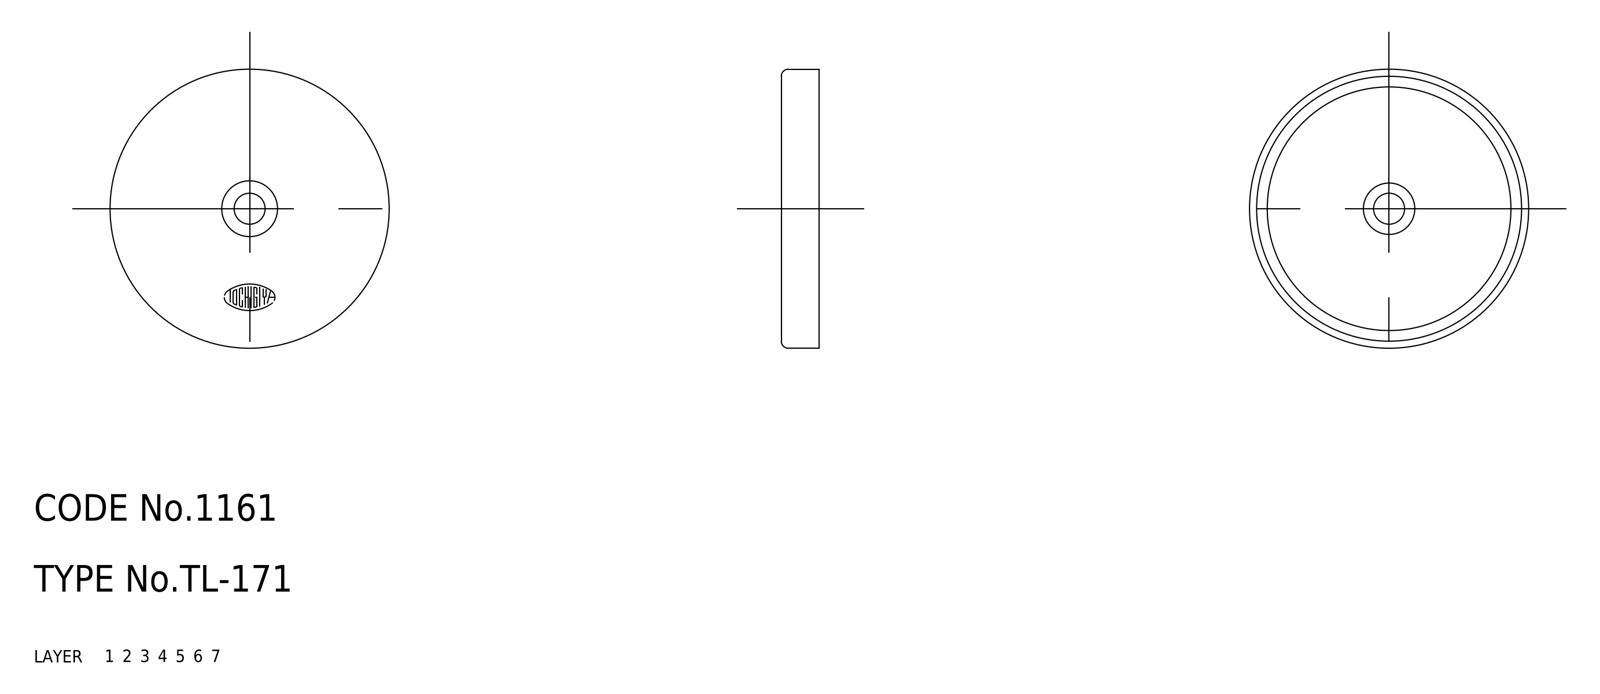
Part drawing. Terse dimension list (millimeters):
name: magnet; housing; TL_171_19167_36
written by: CADfix (AUTOMOTIVE_DESIGN)
unit: mm
bodies: 2 solids, 29 faces (0 planar, 0 cylindrical, 29 other)
size: 31.5 × 31.5 × 4.3
volume: 2 739 mm³; area: 3 714 mm²
